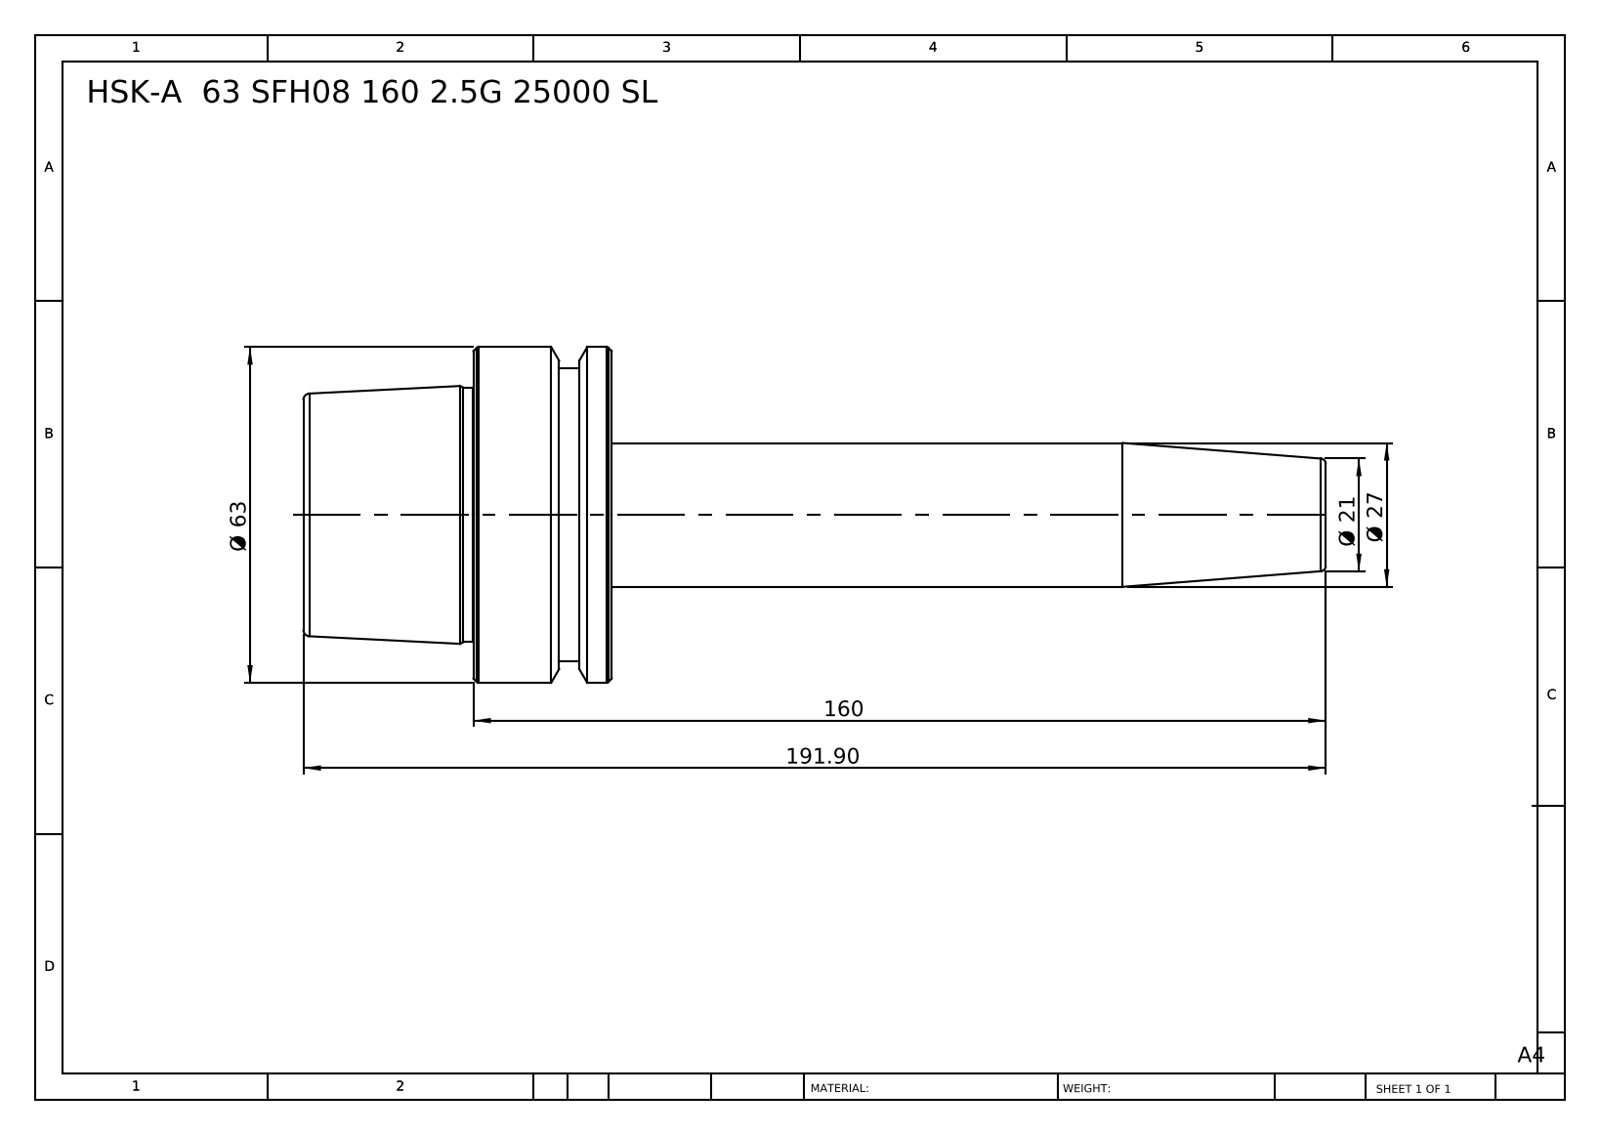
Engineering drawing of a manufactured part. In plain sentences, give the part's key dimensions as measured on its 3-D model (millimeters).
The part is named "HSK-A 63 SFH08 160 2.5G 25000 SL". Its 3-D file was written by "SolidWorks 2014 (CONFIG_CONTROL_DESIGN)". It is 1 solid with 46 faces: 6 planar, 10 cylindrical and 30 other. Overall it measures 191.9 by 63 by 63 millimeters. Its volume is 204 816 cubic millimeters and its surface area 27 415 square millimeters. Round bosses or shafts: 1 of diameter 63, 1 of diameter 55, 1 of diameter 47.78, 1 of diameter 27. The main face-to-face distances are 57.9, 26, 31.9, 134, 160, 191.9, 140.1, 6.1, 19.9, 51.8.
